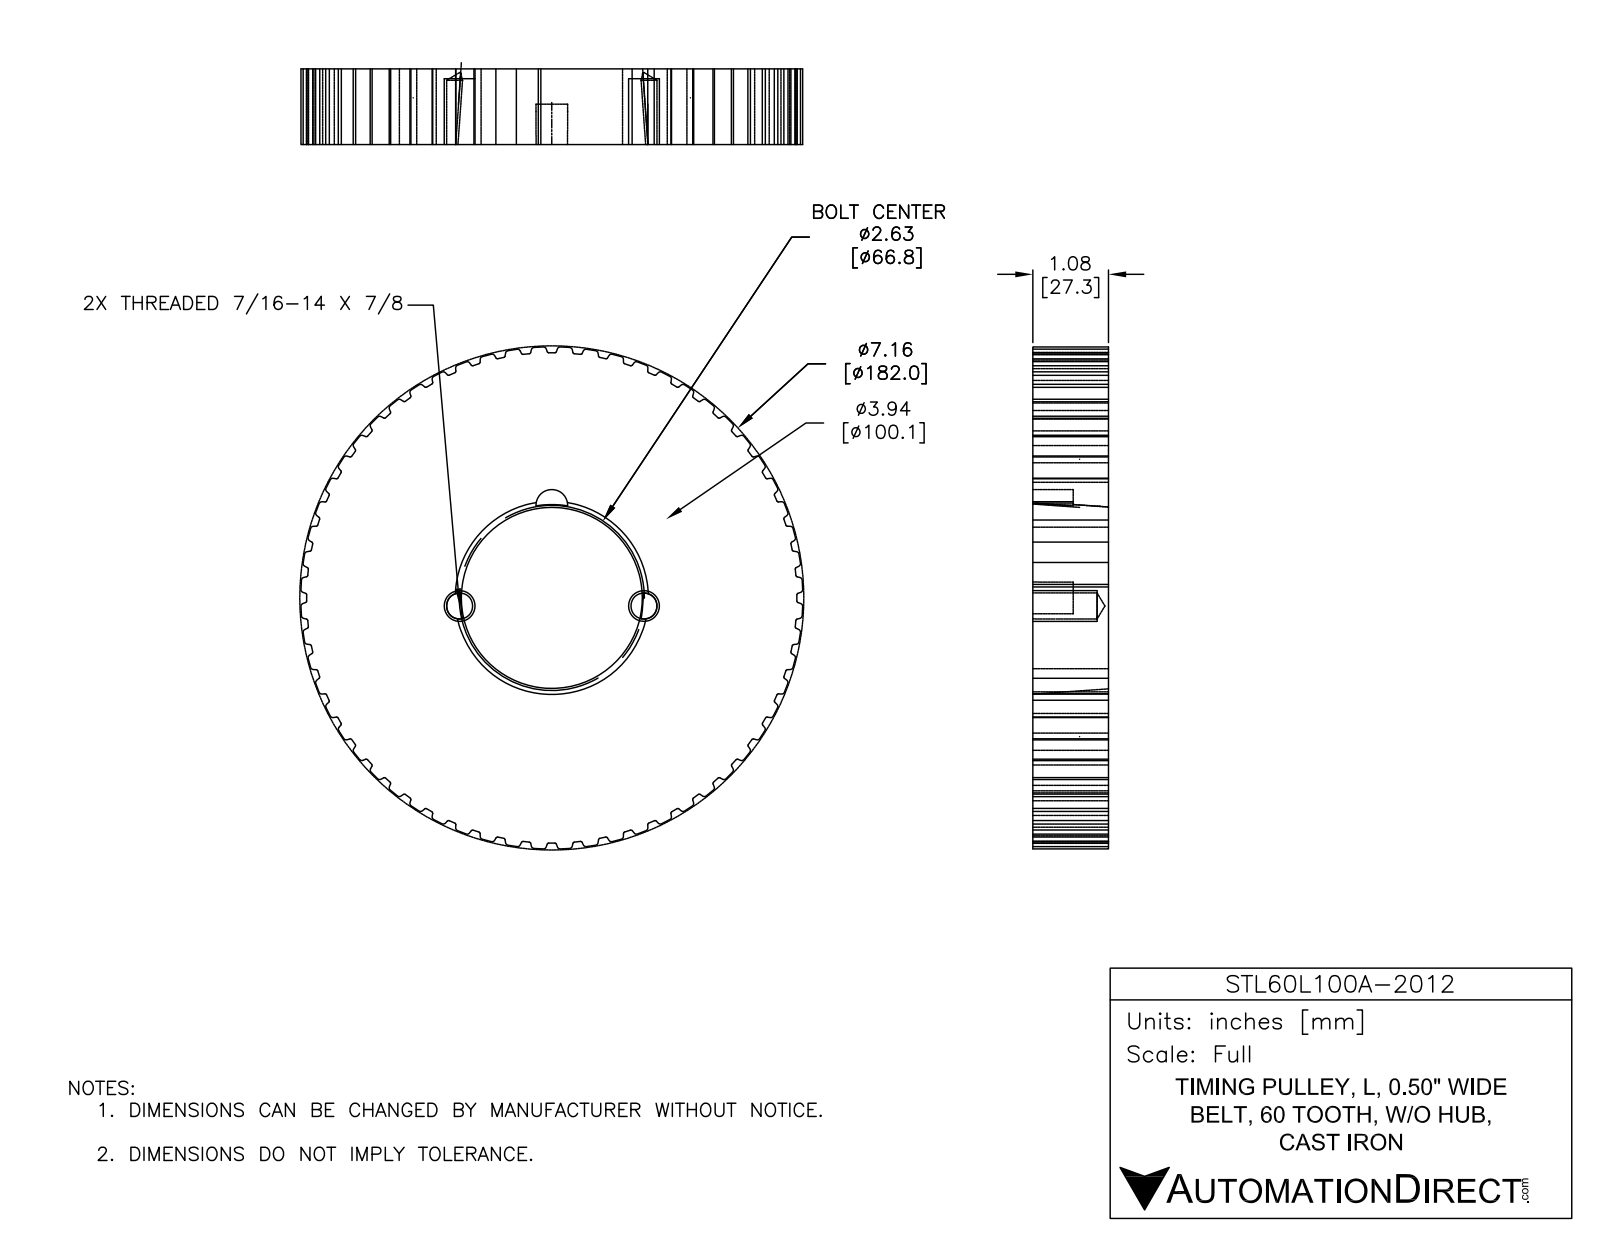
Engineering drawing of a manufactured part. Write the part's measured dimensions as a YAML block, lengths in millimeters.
part_name: "STL60L100A-2012"
step_written_by: "SolidWorks 2018 (AUTOMOTIVE_DESIGN)"
units: millimeters
bodies: {solids: 1, faces: 545, planar: 184, cylindrical: 359, other: 2}
overall_size: [181, 181, 27.29]
volume: 588955
surface_area: 69039
round_bosses_or_shafts:
  - {diameter: 100.1, count: 1}
partial_cylinders:
  - {radius: 0.38, count: 120}
  - {radius: 0.51, count: 120}
  - {radius: 4.7, count: 2}
  - {radius: 5.71, count: 1}
  - {radius: 90.5, count: 1}
face_to_face_distances: [27.26, 27.29, 176.93, 57.63, 176.83, 176.86, 57.61, 57.6, 57.71, 57.68]
